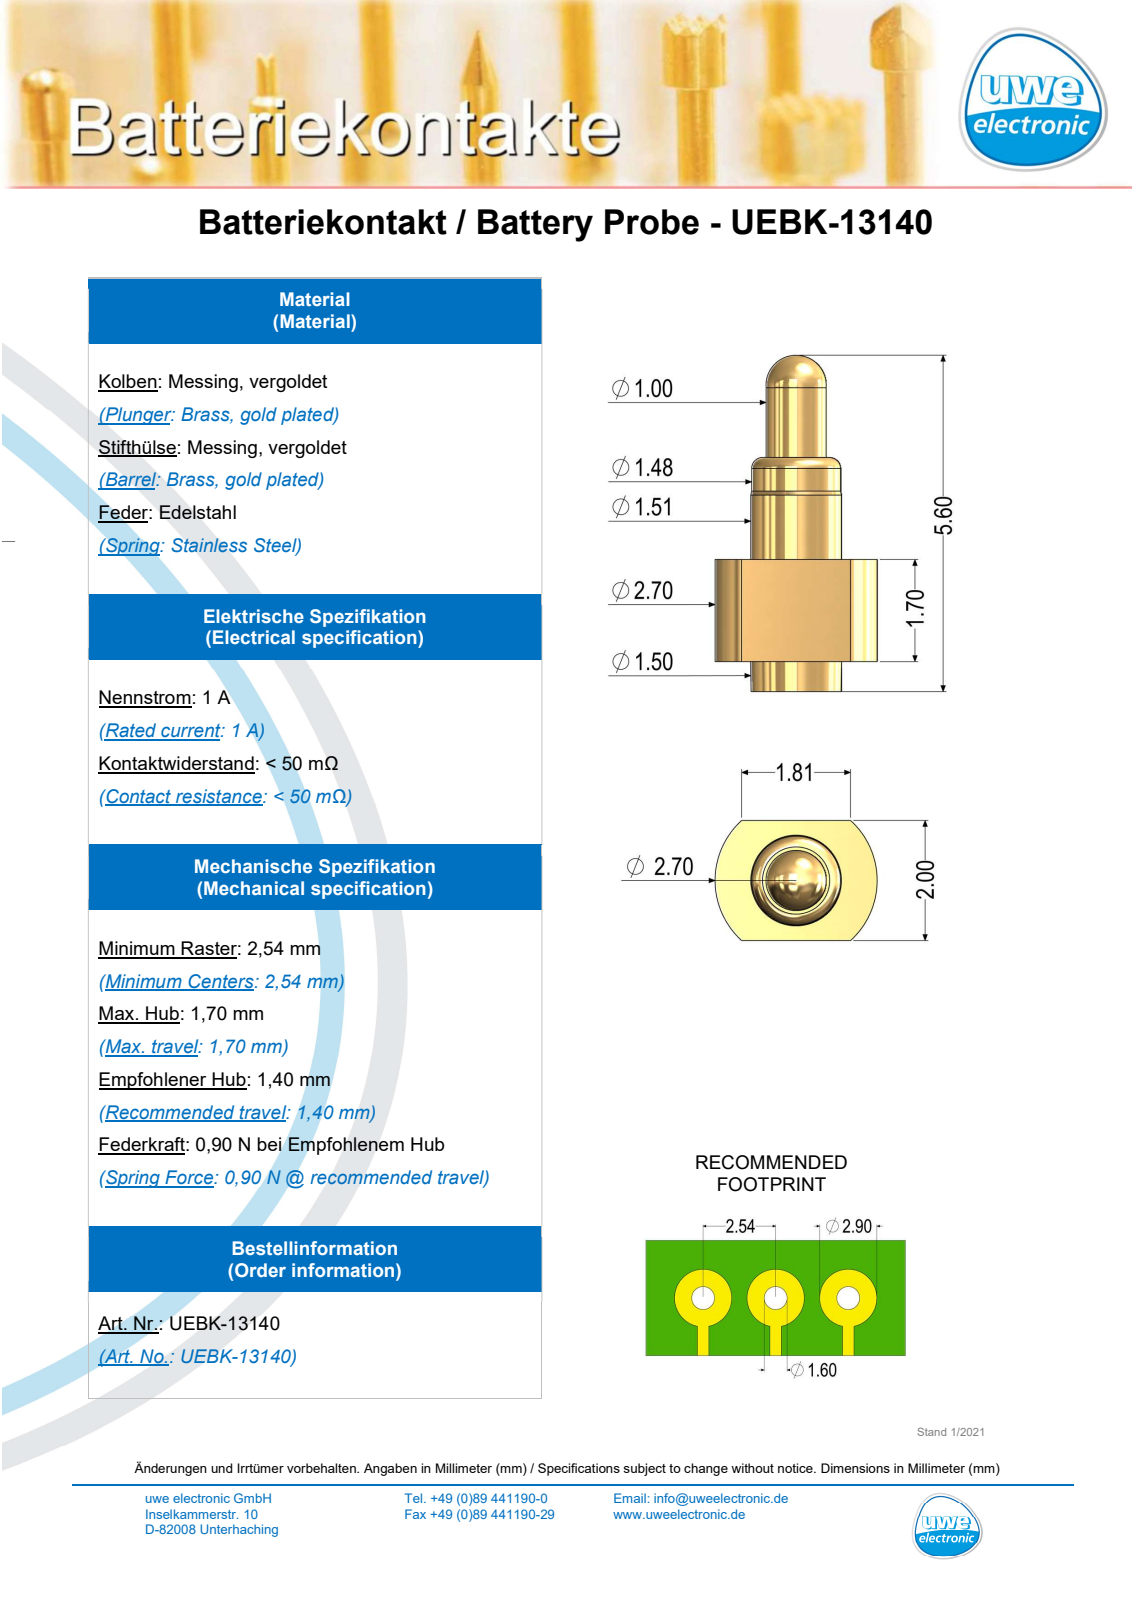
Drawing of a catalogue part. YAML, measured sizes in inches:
part_name: "UEBK-13140_2017_09_05"
step_written_by: "SolidWorks 2017 (AUTOMOTIVE_DESIGN)"
units: inches
bodies: {solids: 1, faces: 23, planar: 6, cylindrical: 9, other: 8}
overall_size: [0.22, 0.106, 0.079]
volume: 0.001
surface_area: 0.059
round_bosses_or_shafts:
  - {diameter: 0.059, count: 1}
  - {diameter: 0.058, count: 1}
  - {diameter: 0.039, count: 1}
partial_cylinders:
  - {radius: 0.053, count: 1}
face_to_face_distances: [0.067, 0.079, 0.02, 0.087, 0.154, 0.134]
